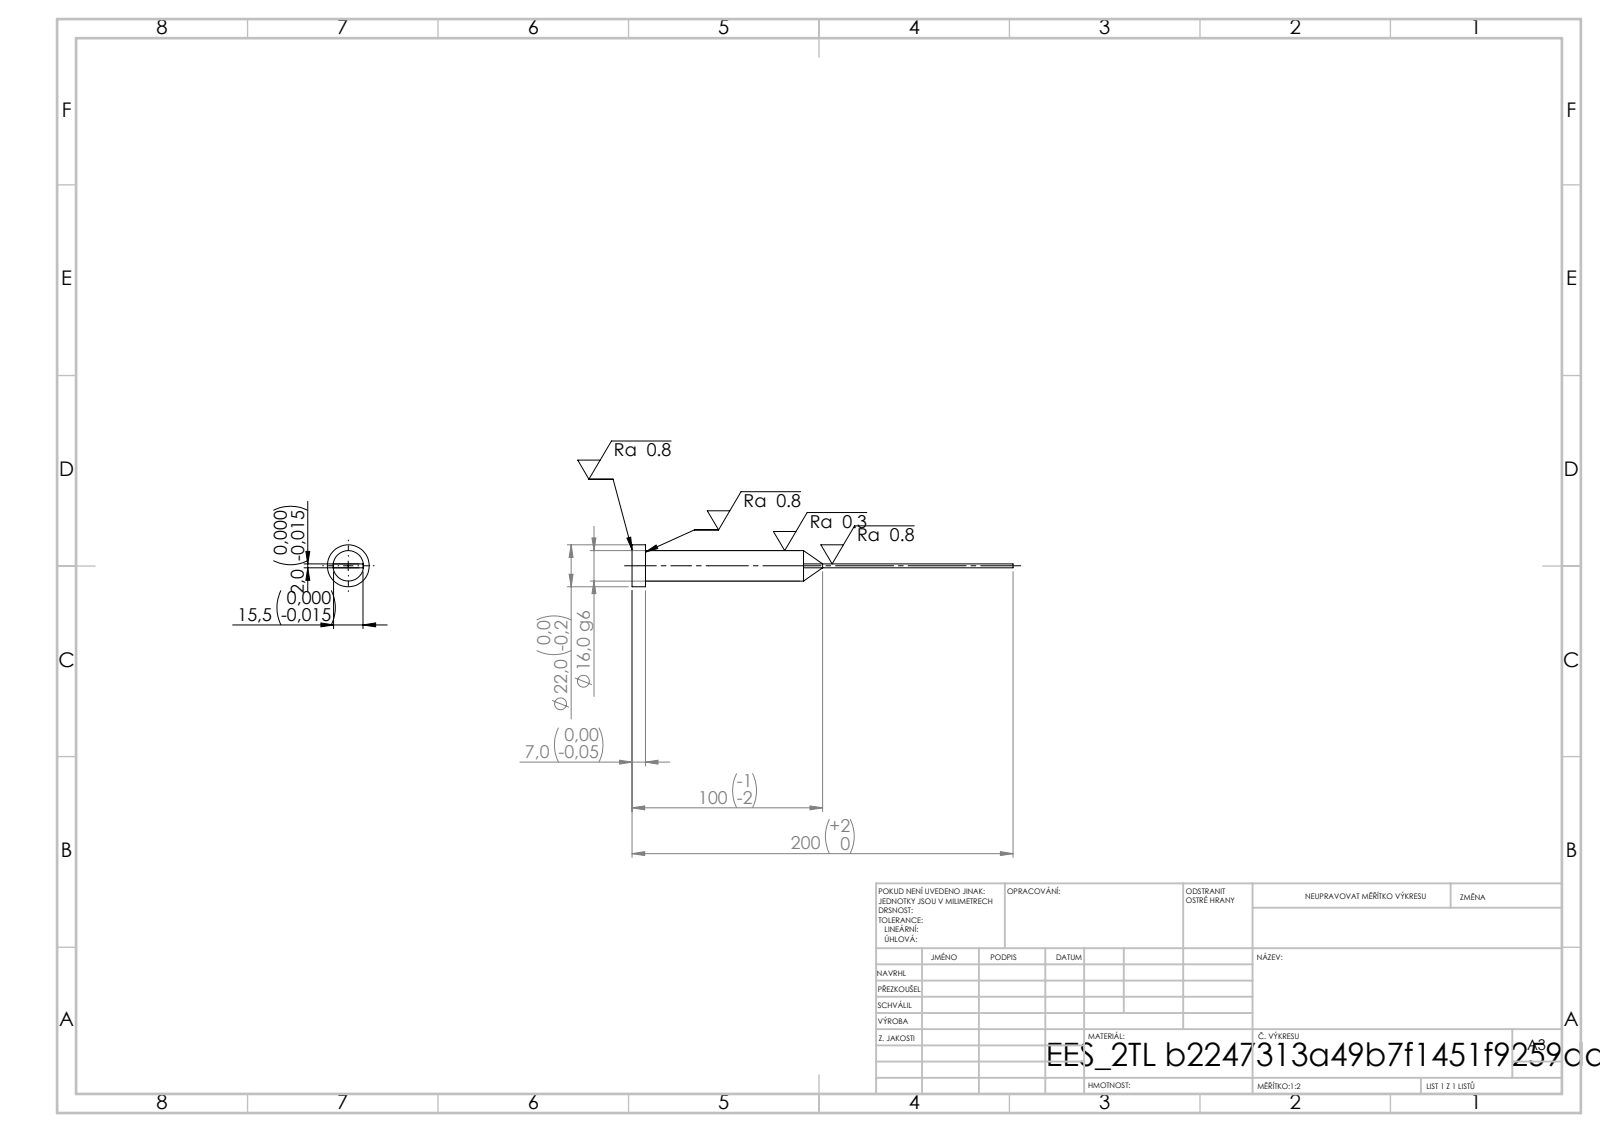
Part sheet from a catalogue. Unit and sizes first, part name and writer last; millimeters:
Units: millimetres
Overall size (bounding box): 200 × 22 × 22
Round bosses / shafts (diameter × count): ⌀22 ×1, ⌀16 ×1
Main face-to-face distances: 2, 15.5, 7, 200, 193
Volume: 23 540 mm³ · Surface area: 9 194 mm²
Bodies: 1 solid, 15 faces (7 planar, 4 cylindrical, 4 other)
STEP written by: SolidWorks 2019 (CONFIG_CONTROL_DESIGN)
